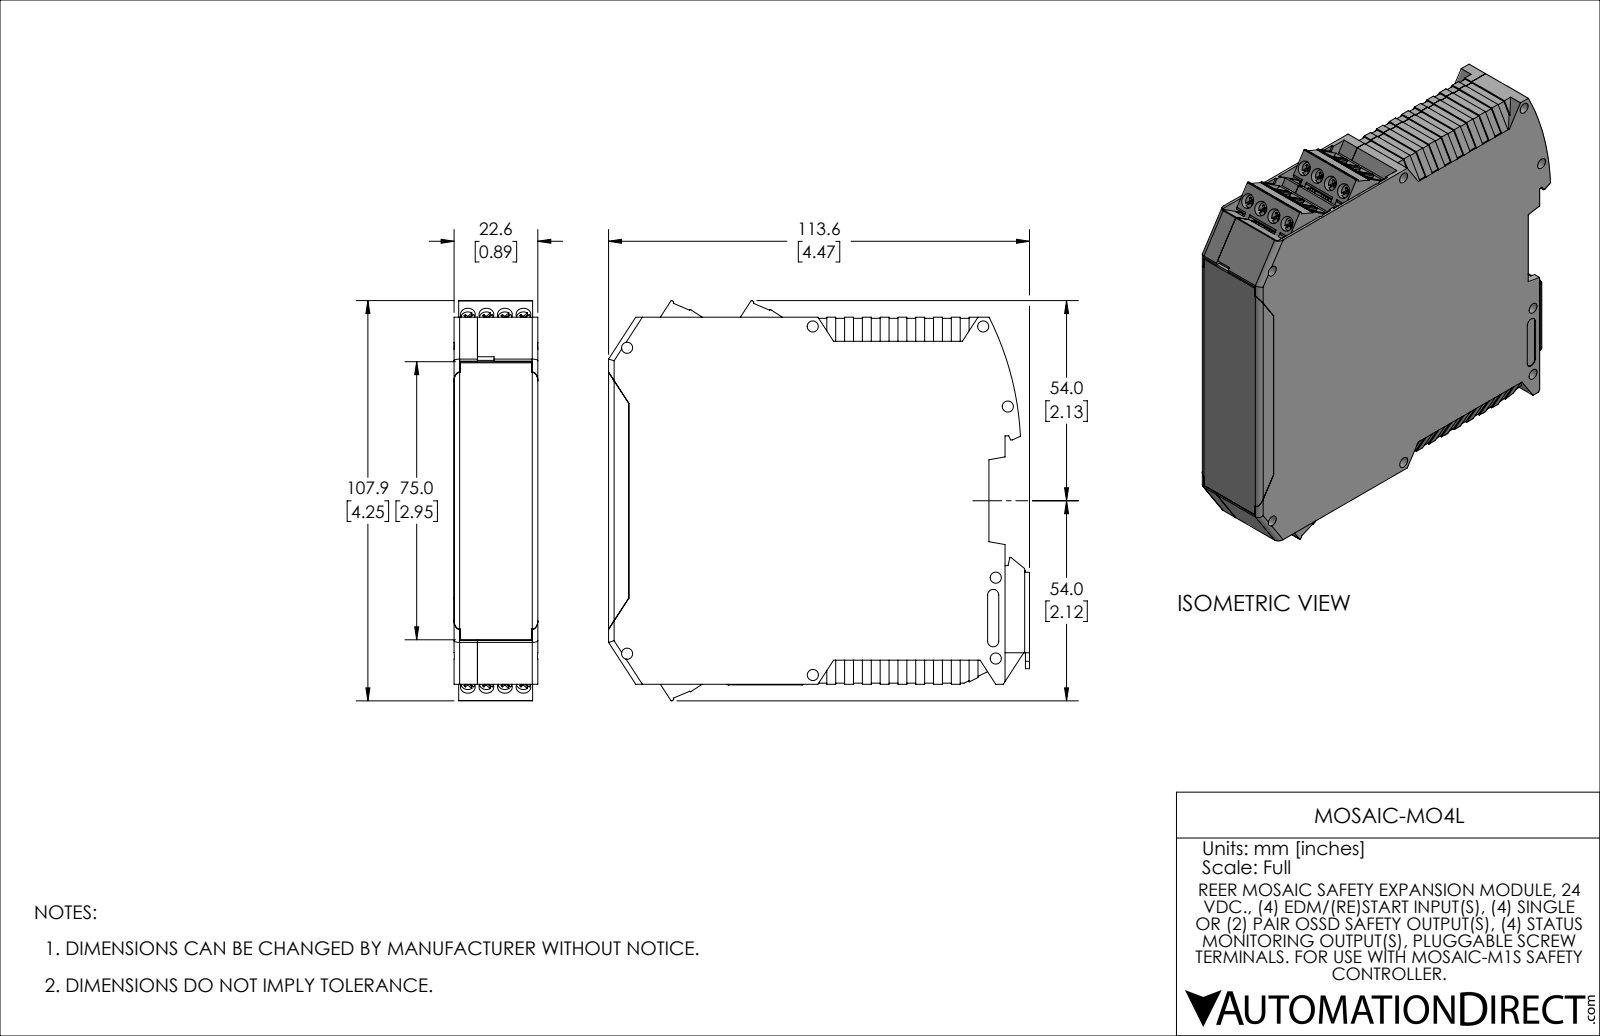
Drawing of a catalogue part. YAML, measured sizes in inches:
part_name: "MOSAIC-MO4L"
step_written_by: "SolidWorks 2021 (AUTOMOTIVE_DESIGN)"
units: inches
bodies: {solids: 9, faces: 1635, planar: 1408, cylindrical: 224, other: 3}
overall_size: [4.472, 4.25, 0.89]
volume: 3.353
surface_area: 115.8
round_holes:
  - {diameter: 0.055, count: 14}
  - {diameter: 0.118, count: 14}
  - {diameter: 0.11, count: 12}
  - {diameter: 0.157, count: 12}
  - {diameter: 0.063, count: 1}
round_bosses_or_shafts:
  - {diameter: 0.149, count: 12}
  - {diameter: 0.177, count: 1}
  - {diameter: 0.11, count: 1}
  - {diameter: 0.053, count: 1}
partial_cylinders:
  - {radius: 0.012, count: 26}
  - {radius: 0.114, count: 12}
  - {radius: 0.03, count: 11}
  - {radius: 0.059, count: 10}
  - {radius: 0.008, count: 9}
  - {radius: 0.031, count: 6}
  - {radius: 0.02, count: 5}
  - {radius: 0.098, count: 5}
face_to_face_distances: [0.049, 0.841, 0.89, 0.791, 0.039, 0.199, 0.642, 0.047, 0.248, 0.593]
hole_center_spacings: [0.197, 0.394, 0.503, 0.591, 0.74, 0.463, 0.608, 0.713]
